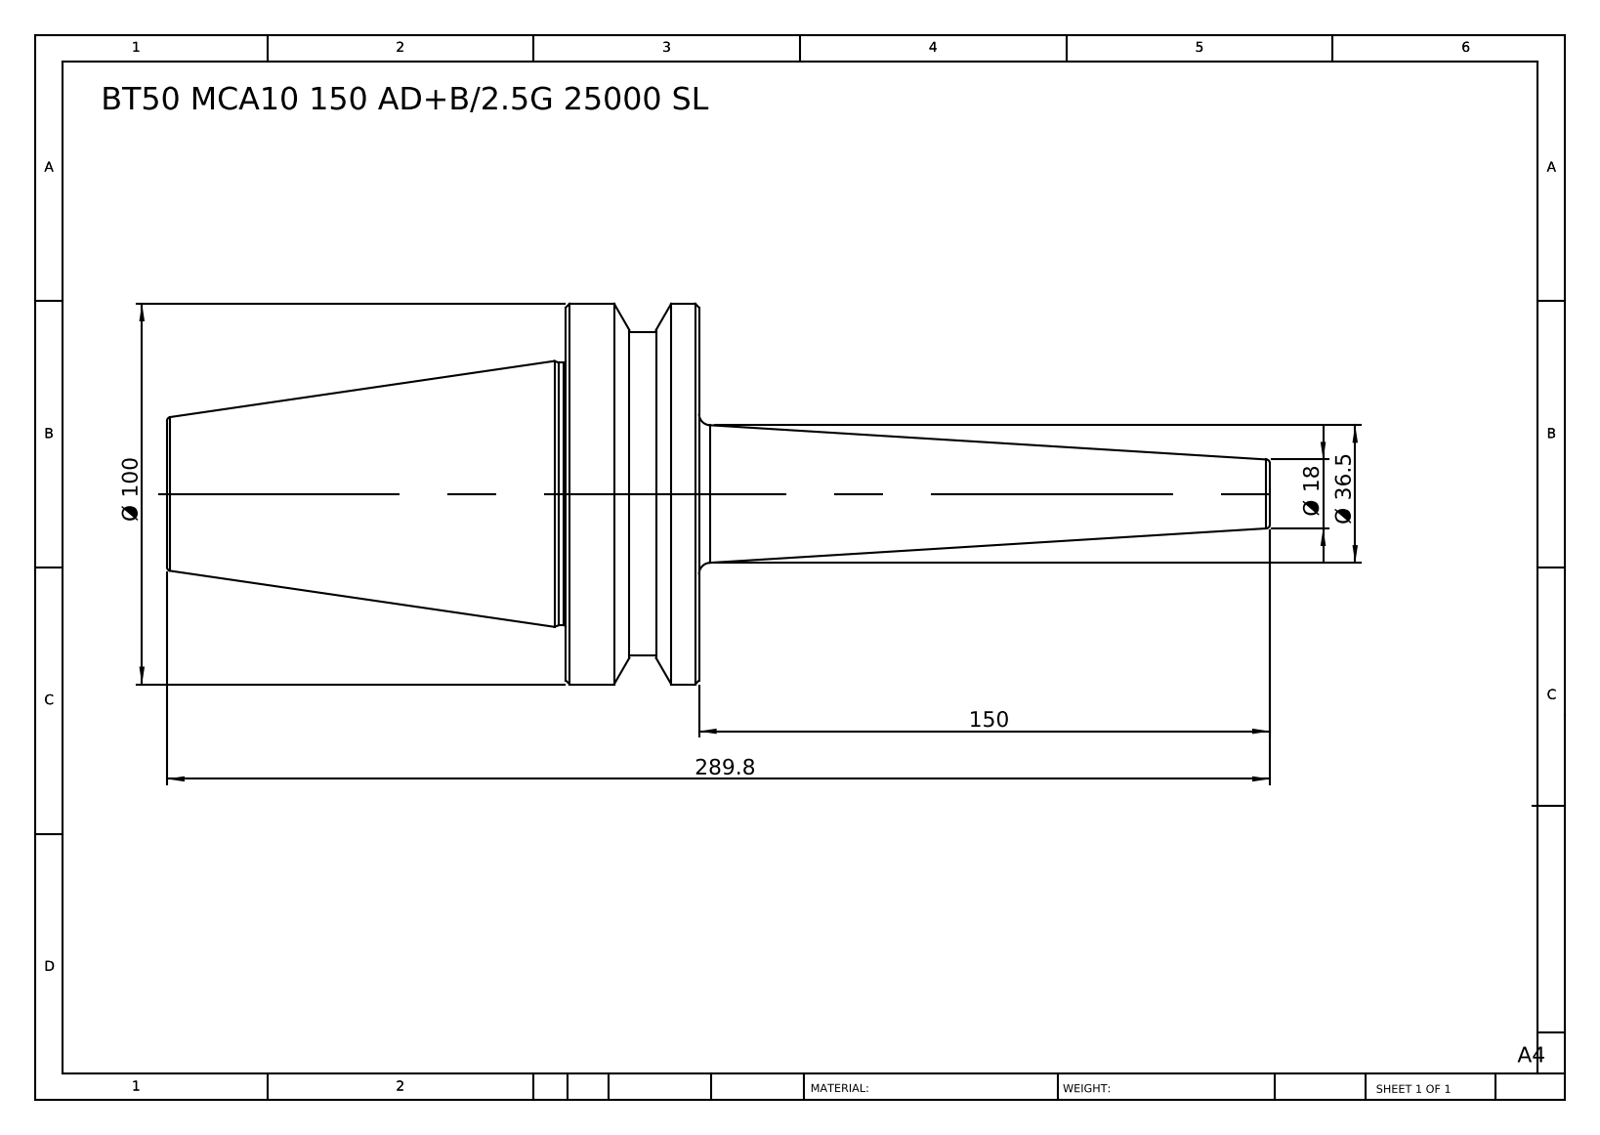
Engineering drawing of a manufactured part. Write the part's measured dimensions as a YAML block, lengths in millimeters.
part_name: "BT50 MCA10 150 AD+B-2.5G 25000 SL"
step_written_by: "SolidWorks 2014 (CONFIG_CONTROL_DESIGN)"
units: millimeters
bodies: {solids: 1, faces: 36, planar: 6, cylindrical: 8, other: 22}
overall_size: [289.8, 100, 100]
volume: 601080
surface_area: 56292
round_bosses_or_shafts:
  - {diameter: 100, count: 1}
  - {diameter: 85, count: 1}
  - {diameter: 69, count: 1}
face_to_face_distances: [35, 139.8, 104.8, 150, 185, 289.8, 161.3, 11.3, 23.7, 128.5]
